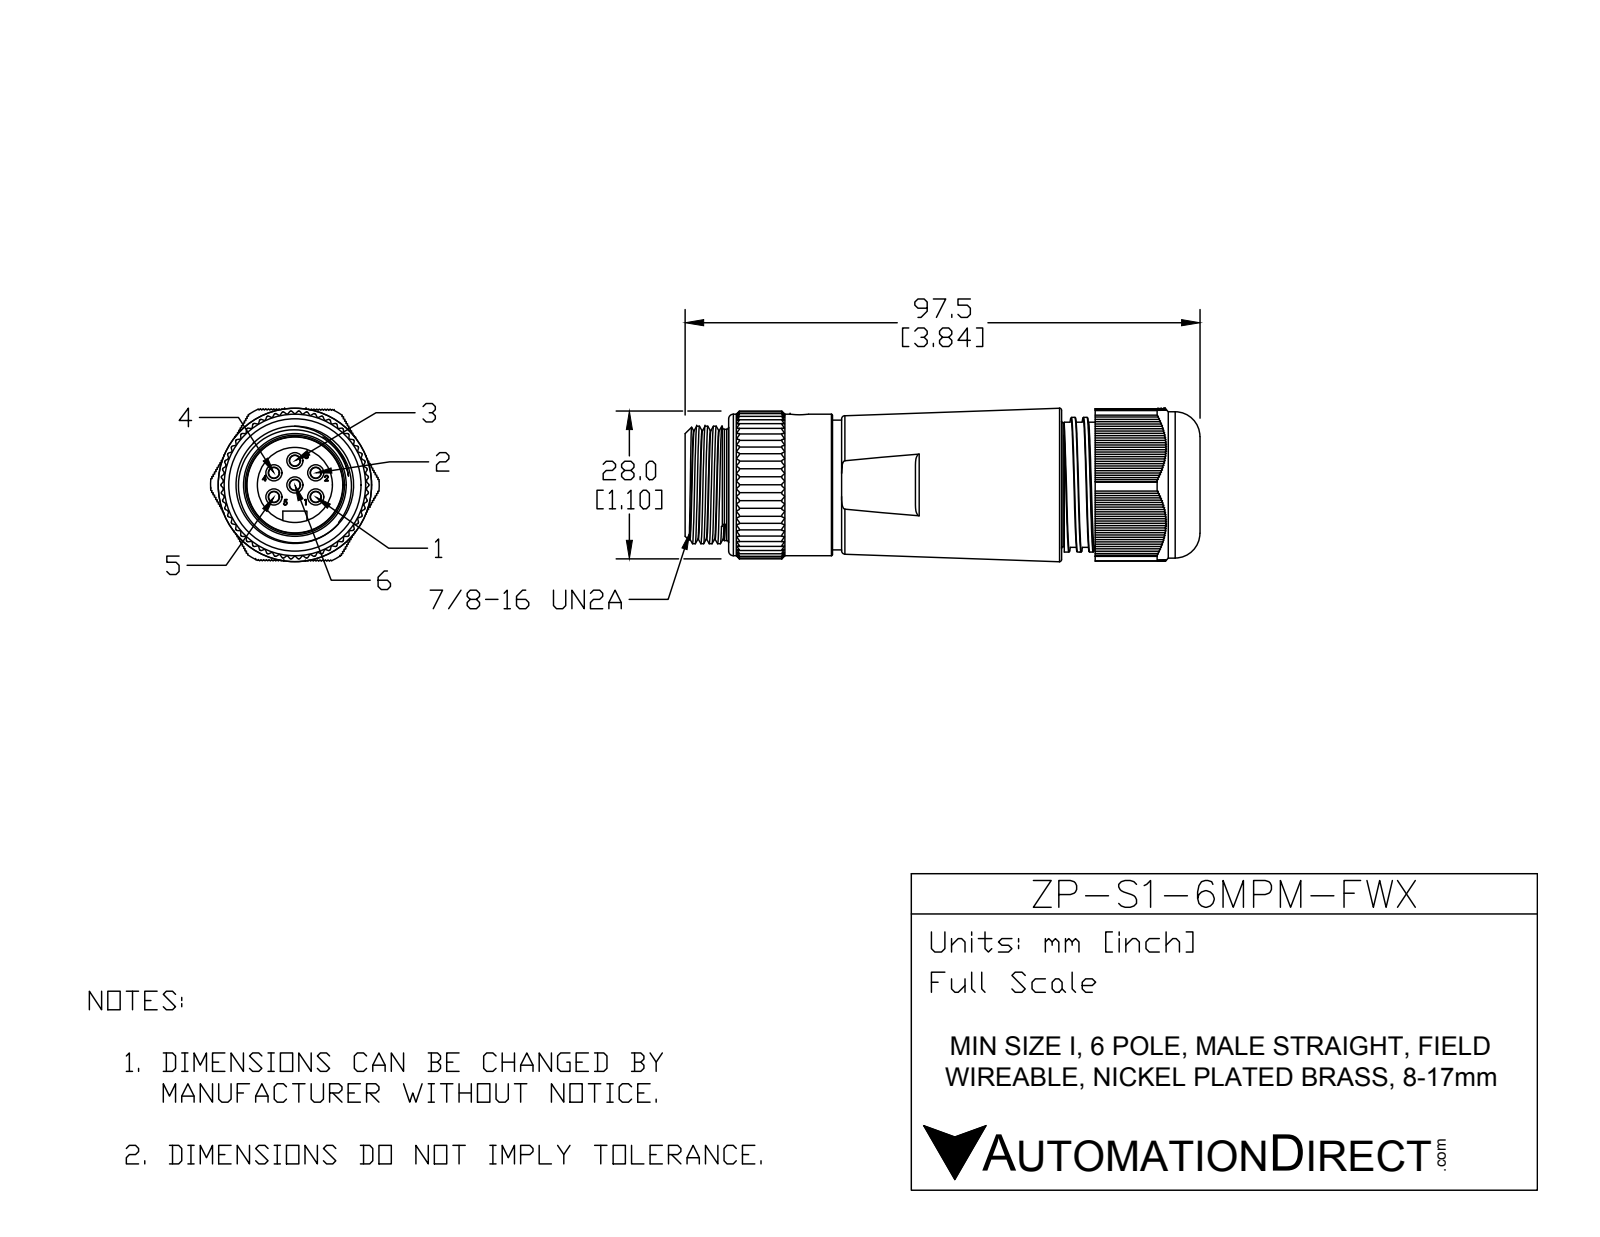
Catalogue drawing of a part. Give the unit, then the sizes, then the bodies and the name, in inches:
Units: inches
Overall size (bounding box): 3.841 × 1.256 × 1.144
Round holes (diameter × count): ⌀0.14 ×1, ⌀0.56 ×1, ⌀0.68 ×1, ⌀0.72 ×1, ⌀0.849 ×1, ⌀0.953 ×1, ⌀1 ×1
Round bosses / shafts (diameter × count): ⌀0.124 ×6, ⌀0.079 ×6, ⌀1.09 ×1, ⌀1.055 ×1, ⌀1.004 ×1, ⌀0.957 ×1, ⌀0.875 ×1, ⌀0.714 ×1
Partial cylindrical surfaces — rounded edges, fillets, slot ends (radius × count): R0.01 ×165, R0.09 ×1, R0.551 ×1, R0.628 ×1
Main face-to-face distances: 2.708, 0.042, 0.014, 0.028, 0.25, 0.056, 0.083, 2.747, 0.07, 0.346
Volume: 3.014 in³ · Surface area: 27.83 in²
Bodies: 10 solids, 961 faces (535 planar, 328 cylindrical, 98 other)
Part name (STEP PRODUCT): ZP-S1-6MPM-FWX
STEP written by: SolidWorks 2015 (AUTOMOTIVE_DESIGN)
